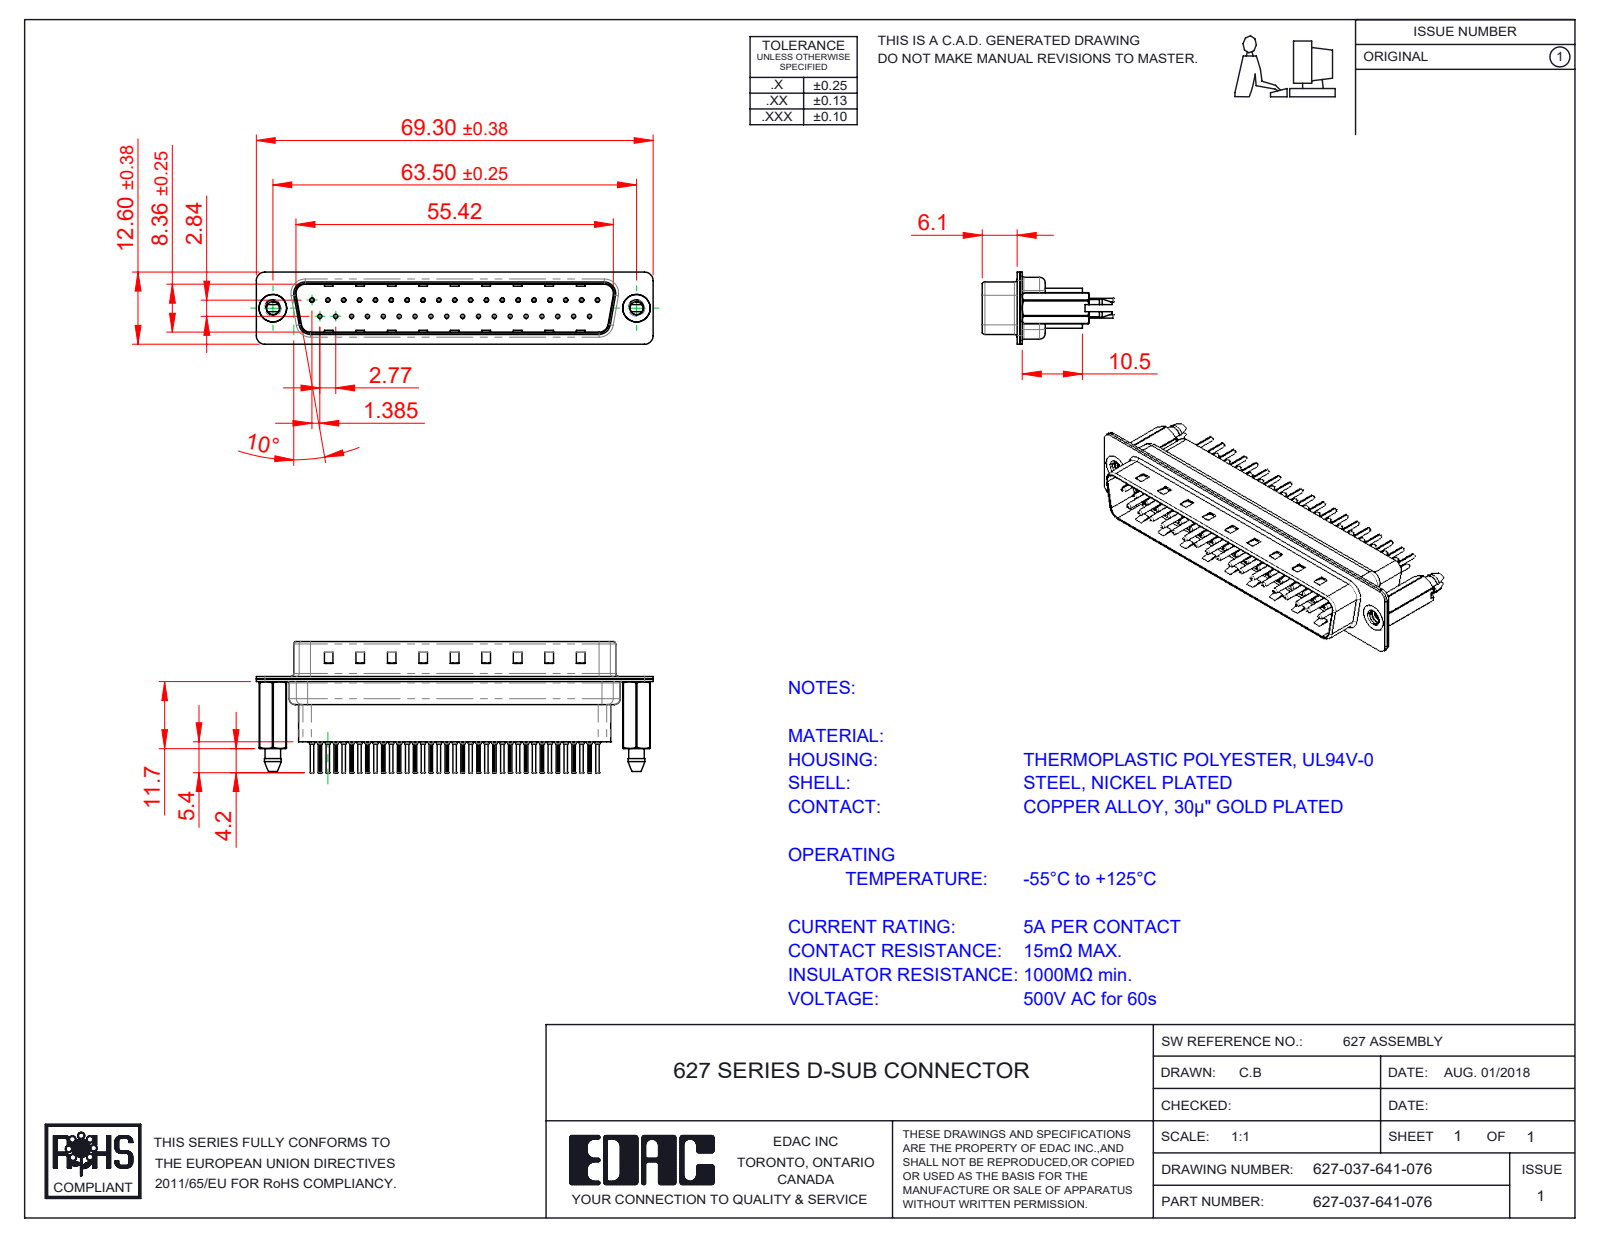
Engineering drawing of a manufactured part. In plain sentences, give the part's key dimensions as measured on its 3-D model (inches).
The part is named "627 Contact Row 2_41; 627 Shell Rear_37 Contacts; 627 Contact Row 1_41; 627 Housing_37 HP (+3 more)". Its 3-D file was written by "SolidWorks 2020 (CONFIG_CONTROL_DESIGN)". It is 42 solids with 4146 faces: 1123 planar, 1576 cylindrical and 1447 other. Overall it measures 2.728 by 0.898 by 0.496 inches. Its volume is 0.342 cubic inches and its surface area 22.32 square inches. Round holes: 37 of diameter 0.008, 37 of diameter 0.014, 37 of diameter 0.043, 37 of diameter 0.063, 2 of diameter 0.089, 2 of diameter 0.157, 2 of diameter 0.189. Round bosses or shafts: 37 of diameter 0.079, 37 of diameter 0.059, 37 of diameter 0.03, 37 of diameter 0.024, 2 of diameter 0.193. Partial cylindrical surfaces (rounded edges, fillets, slot ends): 74 of radius 0.004, 18 of radius 0.059, 12 of radius 0.079, 10 of radius 0.063, 8 of radius 0.02, 4 of radius 0.01, 4 of radius 0.024, 4 of radius 0.026. The main face-to-face distances are 0.016, 0.032, 0.377, 0.027, 0.302, 0.018, 0.059, 0.043, 0.318, 0.345. The hole center spacings are 0.124, 0.109, 0.218, 0.327, 0.198, 0.398, 0.436, 0.503.
